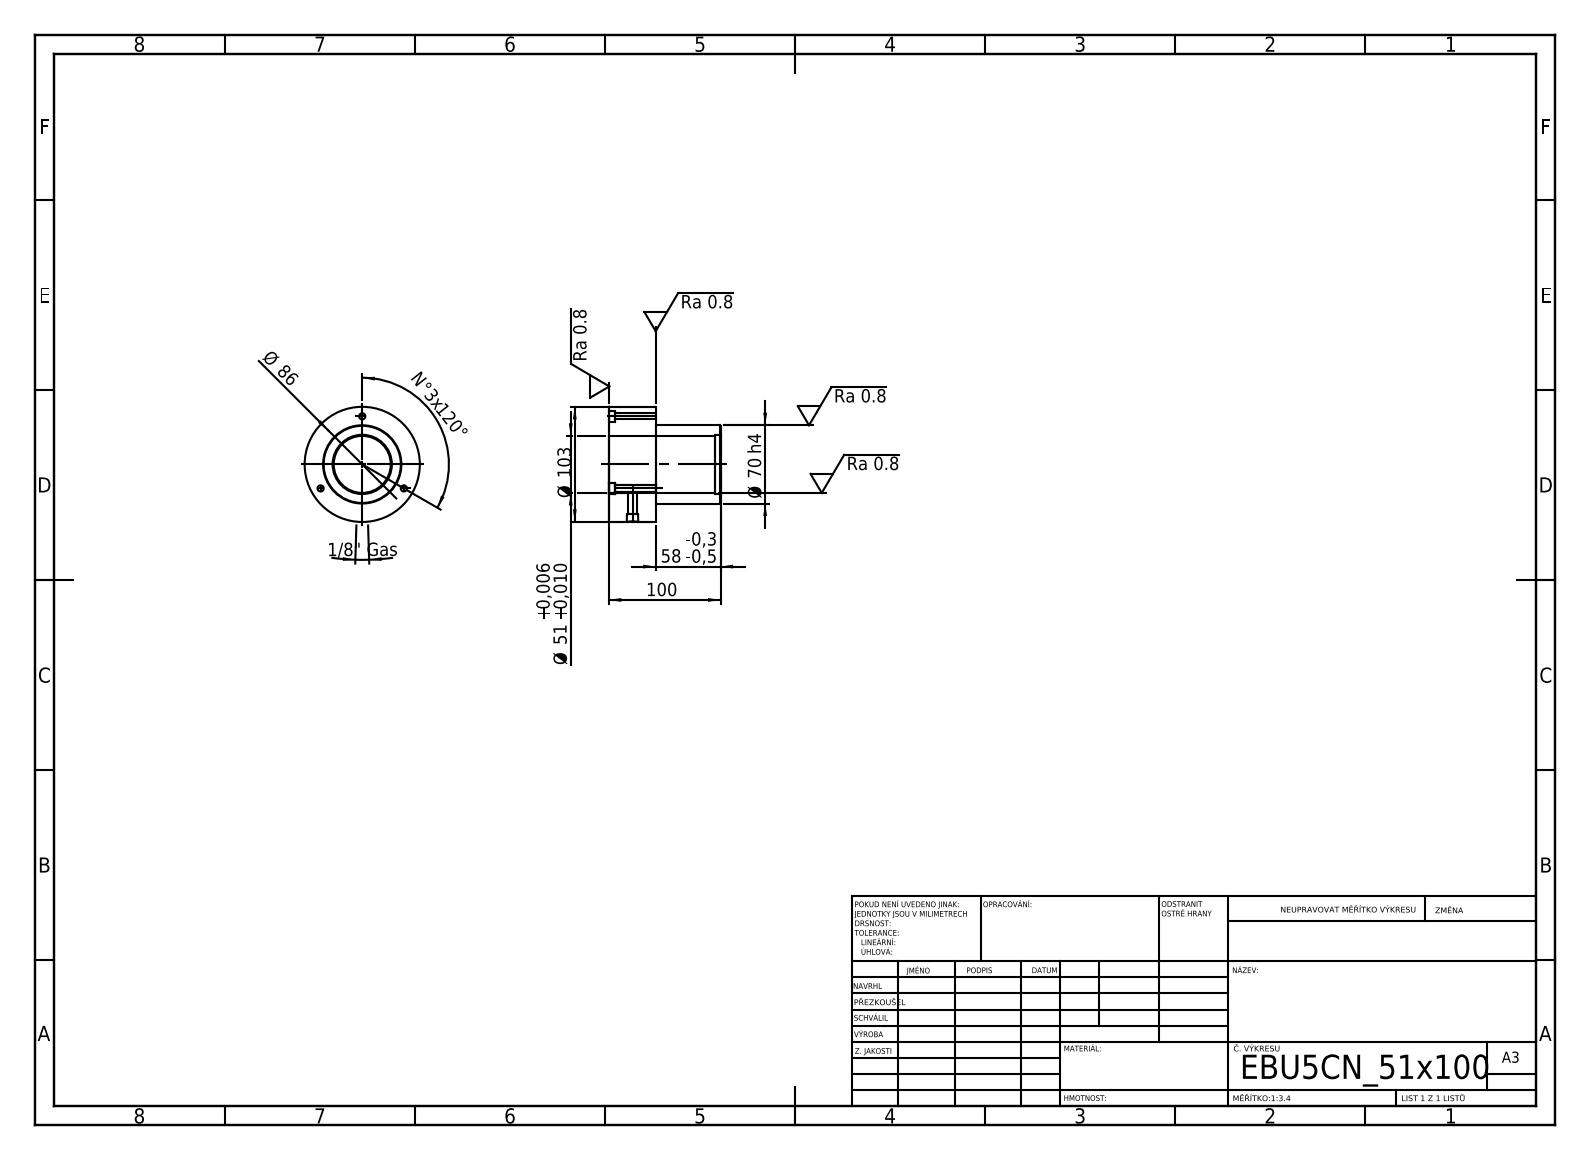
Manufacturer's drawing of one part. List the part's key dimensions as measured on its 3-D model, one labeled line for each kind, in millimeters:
STEP written by: SolidWorks 2019 (CONFIG_CONTROL_DESIGN)
Units: millimetres
Bodies: 1 solid, 36 faces (8 planar, 22 cylindrical, 6 other)
Overall size (bounding box): 103 × 103 × 100
Volume: 362 500 mm³ · Surface area: 57 688 mm²
Round holes (diameter × count): ⌀5.5 ×3, ⌀10 ×3, ⌀8.43 ×1, ⌀51 ×1, ⌀53 ×1
Round bosses / shafts (diameter × count): ⌀103 ×1, ⌀70 ×1
Main face-to-face distances: 42, 58, 100, 94.6, 36.6, 5.4, 5, 53, 89.6, 95
Hole centre spacings: 43, 74.48
